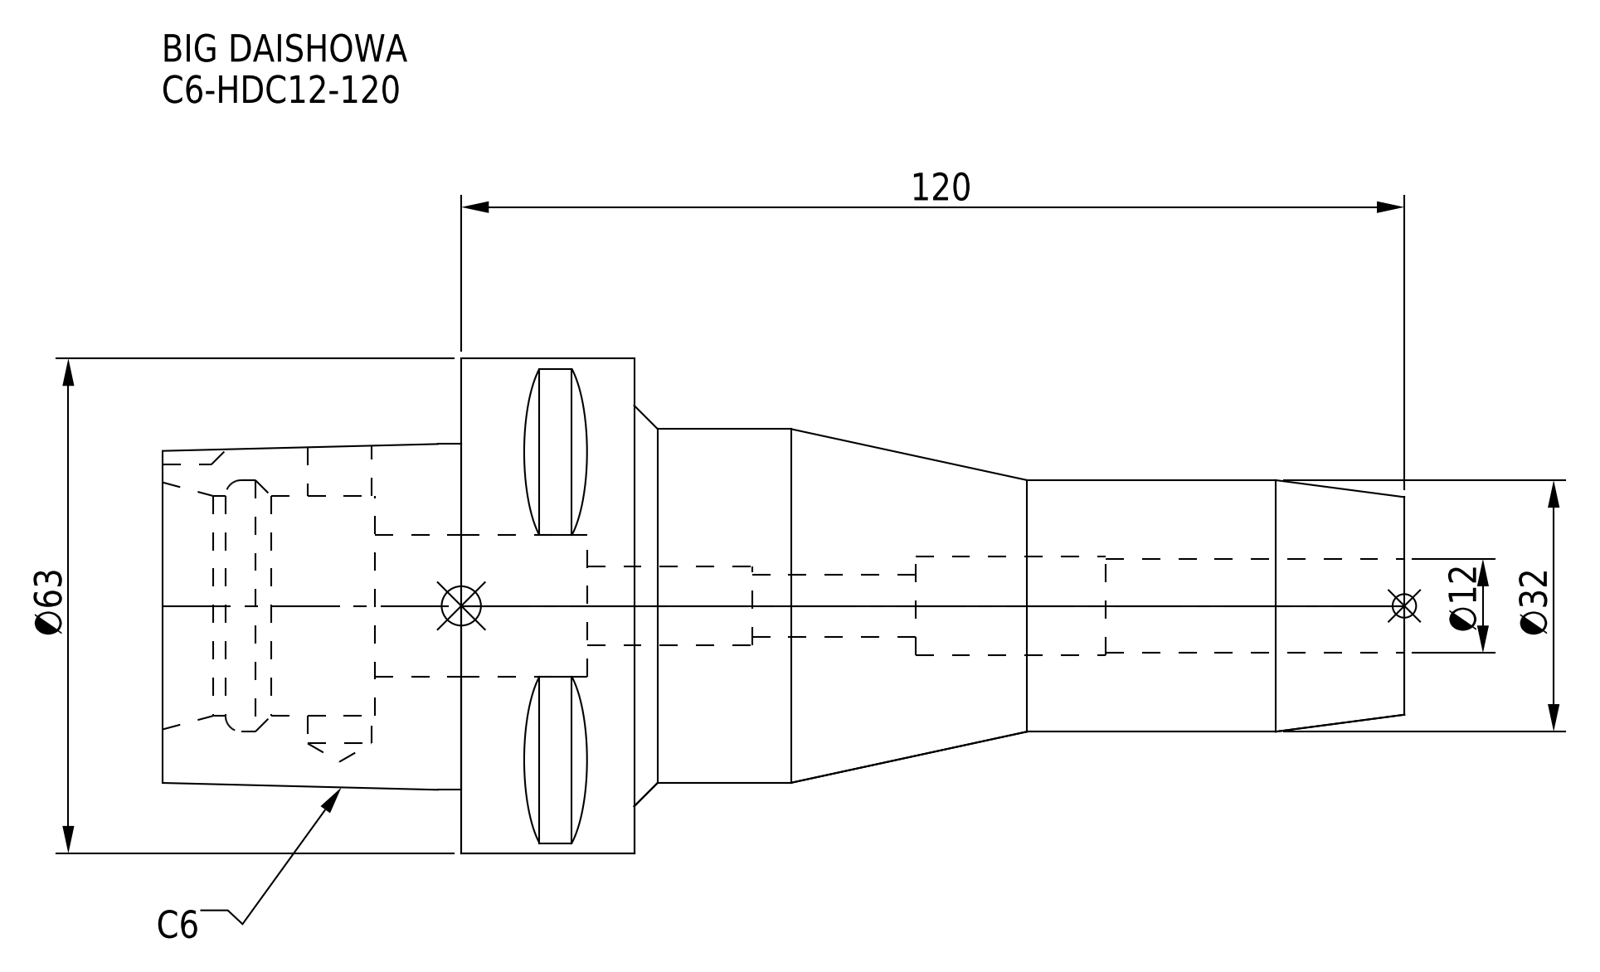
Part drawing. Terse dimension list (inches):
name: C6-HDC12-120
written by: CREO PARAMETRIC BY PTC INC, 2016380 (AUTOMOTIVE_DESIGN)
unit: in
bodies: 1 solid, 74 faces (31 planar, 27 cylindrical, 16 other)
size: 6.22 × 2.48 × 2.48
volume: 11.67 in³; area: 52.2 in²
holes: 1× ⌀0.315, 1× ⌀0.319, 1× ⌀0.394, 1× ⌀0.472, 1× ⌀0.492, 1× ⌀0.709, 1× ⌀1.102, 1× ⌀1.26
bosses: 1× ⌀2.48, 1× ⌀1.772
rounds: 1× R0.197
face distances: 0.866, 1.063, 1.496, 2.362, 4.724, 3.858, 6.22, 5.157, 1.299, 0.433
